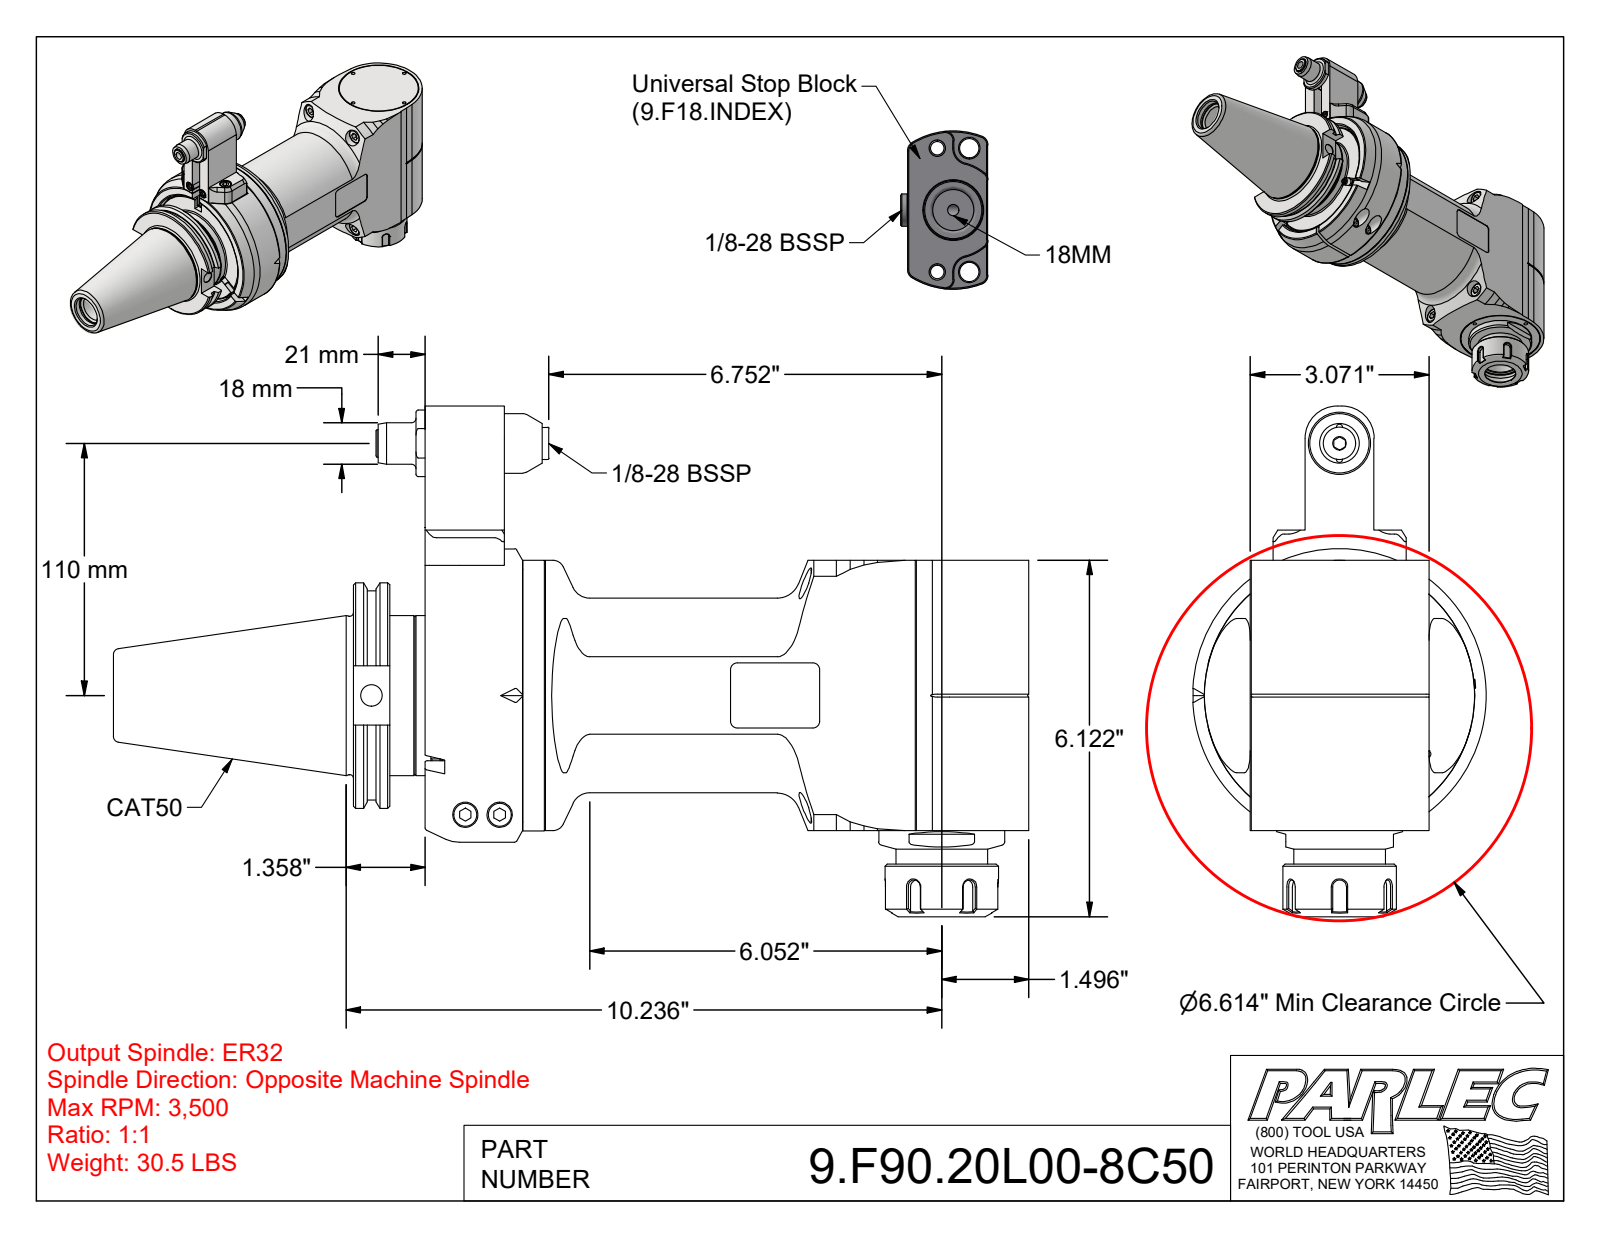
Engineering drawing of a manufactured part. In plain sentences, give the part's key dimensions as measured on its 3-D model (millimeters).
The part is named "9.F90.20L00-8C50; 9GA21C_451 (Type 2, Cat50, 110mm); 9FL2ATC; 9CT502ATC (+6 more)". Its 3-D file was written by "Autodesk Inventor 2022 (AUTOMOTIVE_DESIGN)". It is 8 solids with 671 faces: 318 planar, 151 cylindrical and 202 other. Overall it measures 399.6 by 222.8 by 128 millimeters. Its volume is 2 571 000 cubic millimeters and its surface area 261 800 square millimeters. Round holes: 4 of diameter 3.2, 4 of diameter 5, 4 of diameter 13.5, 2 of diameter 2.6, 2 of diameter 4.2, 2 of diameter 5.3, 2 of diameter 8, 2 of diameter 10.4, 2 of diameter 11, 2 of diameter 27, 1 of diameter 2.5, 1 of diameter 3. Round bosses or shafts: 4 of diameter 13, 4 of diameter 10, 4 of diameter 6, 2 of diameter 18, 2 of diameter 2.5, 1 of diameter 128, 1 of diameter 118.1, 1 of diameter 118. Partial cylindrical surfaces (rounded edges, fillets, slot ends): 8 of radius 2, 7 of radius 3, 4 of radius 4, 2 of radius 0.4, 2 of radius 0.5, 2 of radius 1, 2 of radius 3.5, 2 of radius 8. The main face-to-face distances are 78, 26, 8, 0.5, 9, 35, 6, 16.5, 34, 34.5. The hole center spacings are 31.5, 44.6, 56, 7, 23.4, 37.6, 41, 47.9.
